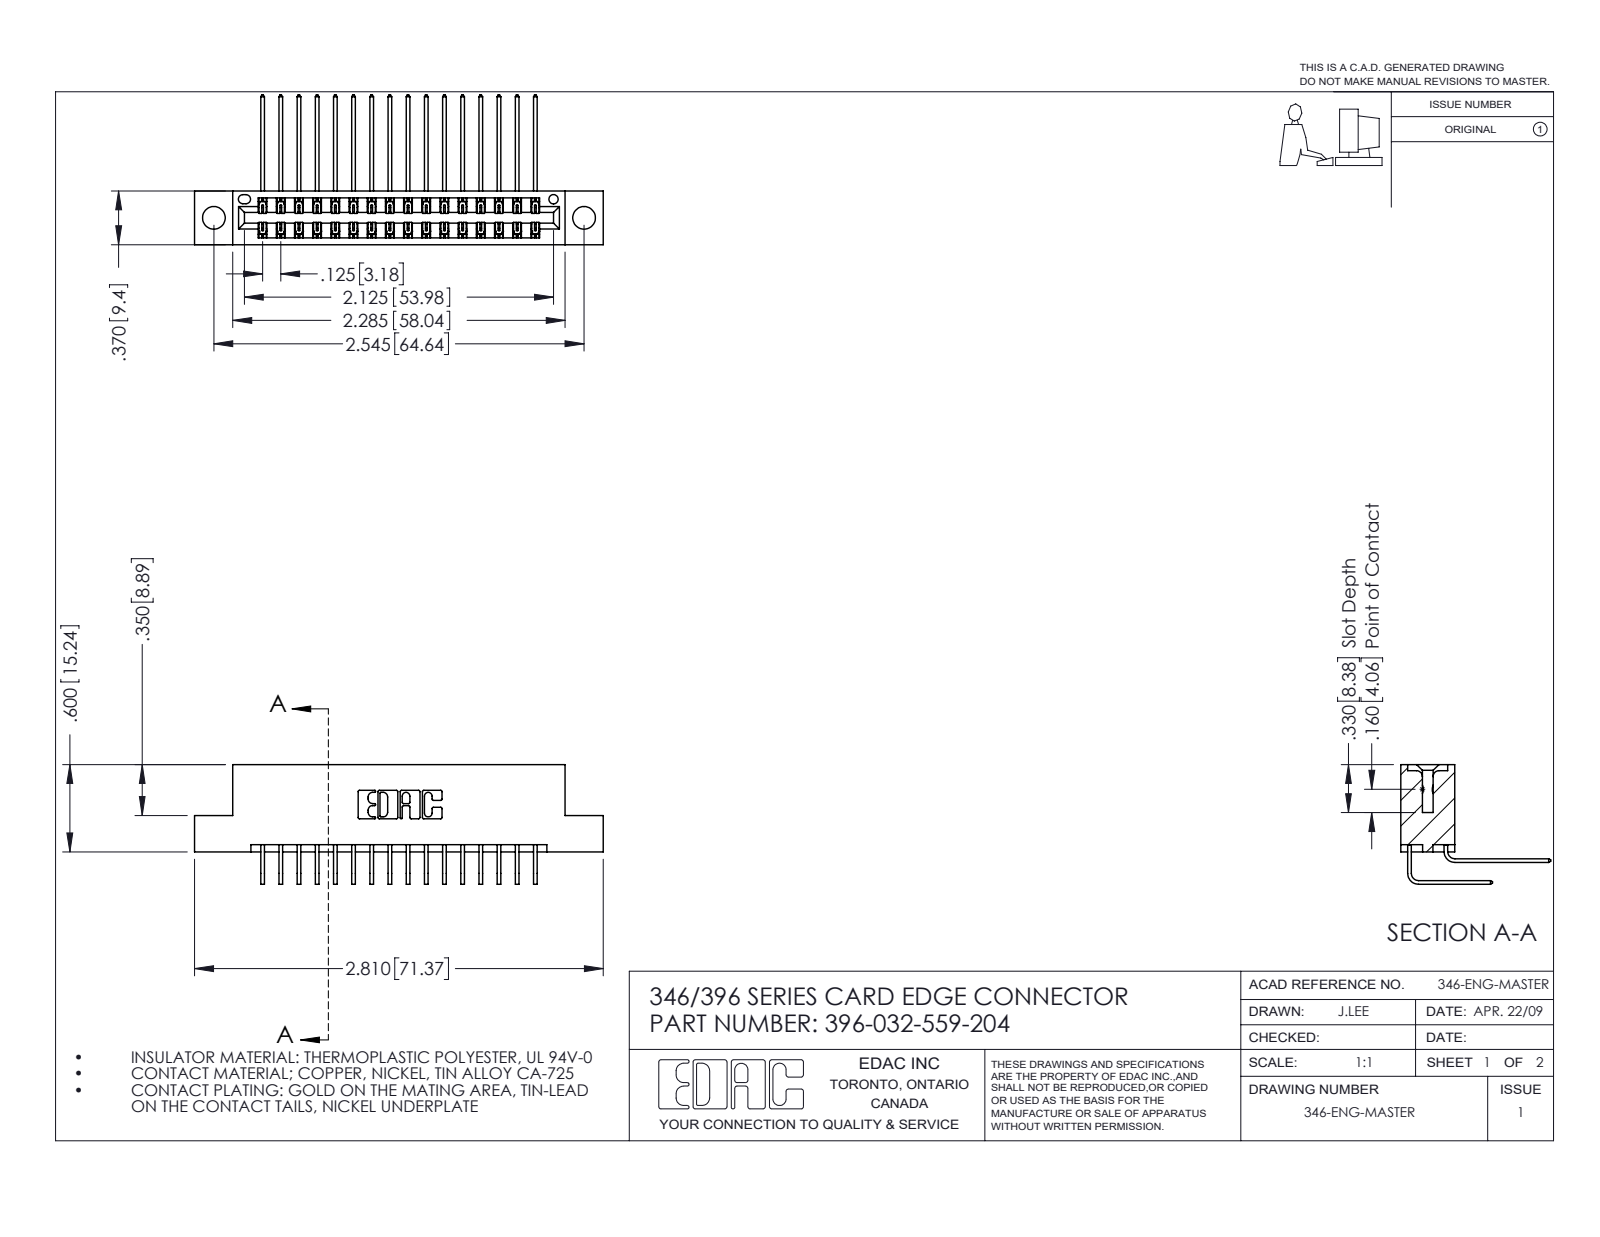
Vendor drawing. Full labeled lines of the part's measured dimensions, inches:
Part name (STEP PRODUCT): 346 Part_Flush Mounting Lugs - 0.156 Dia-TH; 345-292-001_558 559 Tail - 1; 396-032-559-204; 345-292-001_559 Tail - 2
STEP written by: SolidWorks 2016 (CONFIG_CONTROL_DESIGN)
Units: inches
Bodies: 33 solids, 1850 faces (1260 planar, 590 cylindrical, 0 other)
Overall size (bounding box): 2.81 × 1.03 × 0.823
Volume: 0.418 in³ · Surface area: 15.05 in²
Round holes (diameter × count): ⌀0.156 ×2, ⌀0.064 ×1
Partial cylindrical surfaces — rounded edges, fillets, slot ends (radius × count): R0.006 ×48, R0.01 ×22, R0.007 ×6, R0.031 ×6, R0.026 ×3, R0.014 ×2, R0.022 ×2, R0.024 ×2
Main face-to-face distances: 0.048, 0.322, 0.25, 0.025, 0.37, 0.072, 0.298, 0.275, 0.148, 0.222
Hole centre spacings: 0.246, 2.338, 2.545
